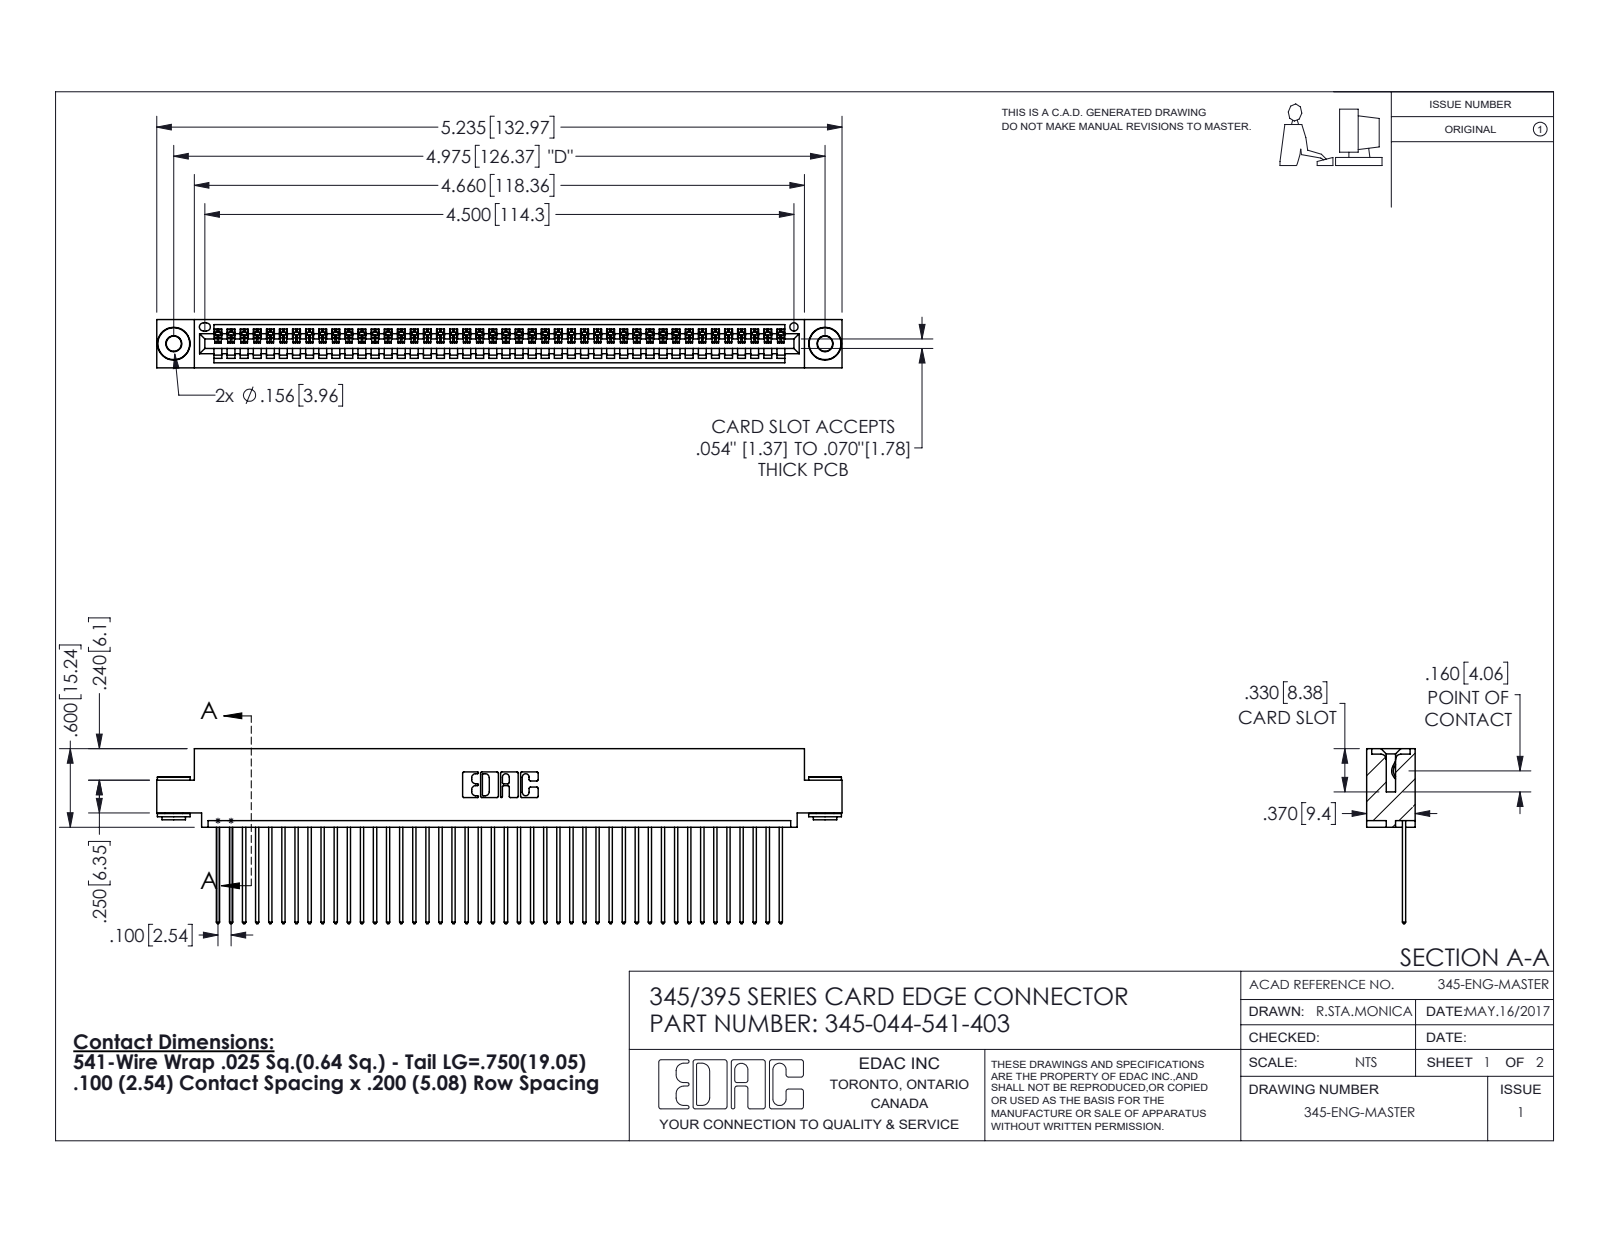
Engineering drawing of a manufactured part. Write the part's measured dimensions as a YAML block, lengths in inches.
part_name: "345 Part_0.110 Offset - 0.156 Dia-TH; 345-044-541-403; 345-250-002_345-250-002-102; 345-292-001_345-293-141"
step_written_by: "SolidWorks 2016 (CONFIG_CONTROL_DESIGN)"
units: inches
bodies: {solids: 47, faces: 2720, planar: 1854, cylindrical: 858, other: 8}
overall_size: [5.235, 1.337, 0.37]
volume: 0.777
surface_area: 28.06
round_holes:
  - {diameter: 0.116, count: 2}
  - {diameter: 0.156, count: 2}
  - {diameter: 0.064, count: 1}
round_bosses_or_shafts:
  - {diameter: 0.25, count: 2}
  - {diameter: 0.18, count: 2}
  - {diameter: 0.136, count: 2}
partial_cylinders:
  - {radius: 0.006, count: 88}
  - {radius: 0.01, count: 88}
  - {radius: 0.01, count: 22}
  - {radius: 0.007, count: 6}
  - {radius: 0.031, count: 6}
  - {radius: 0.026, count: 3}
  - {radius: 0.031, count: 2}
  - {radius: 0.04, count: 2}
face_to_face_distances: [0.072, 0.298, 0.025, 0.098, 0.272, 0.37, 0.2, 0.225, 0.149, 0.072]
hole_center_spacings: [0.27, 4.739, 4.975]
